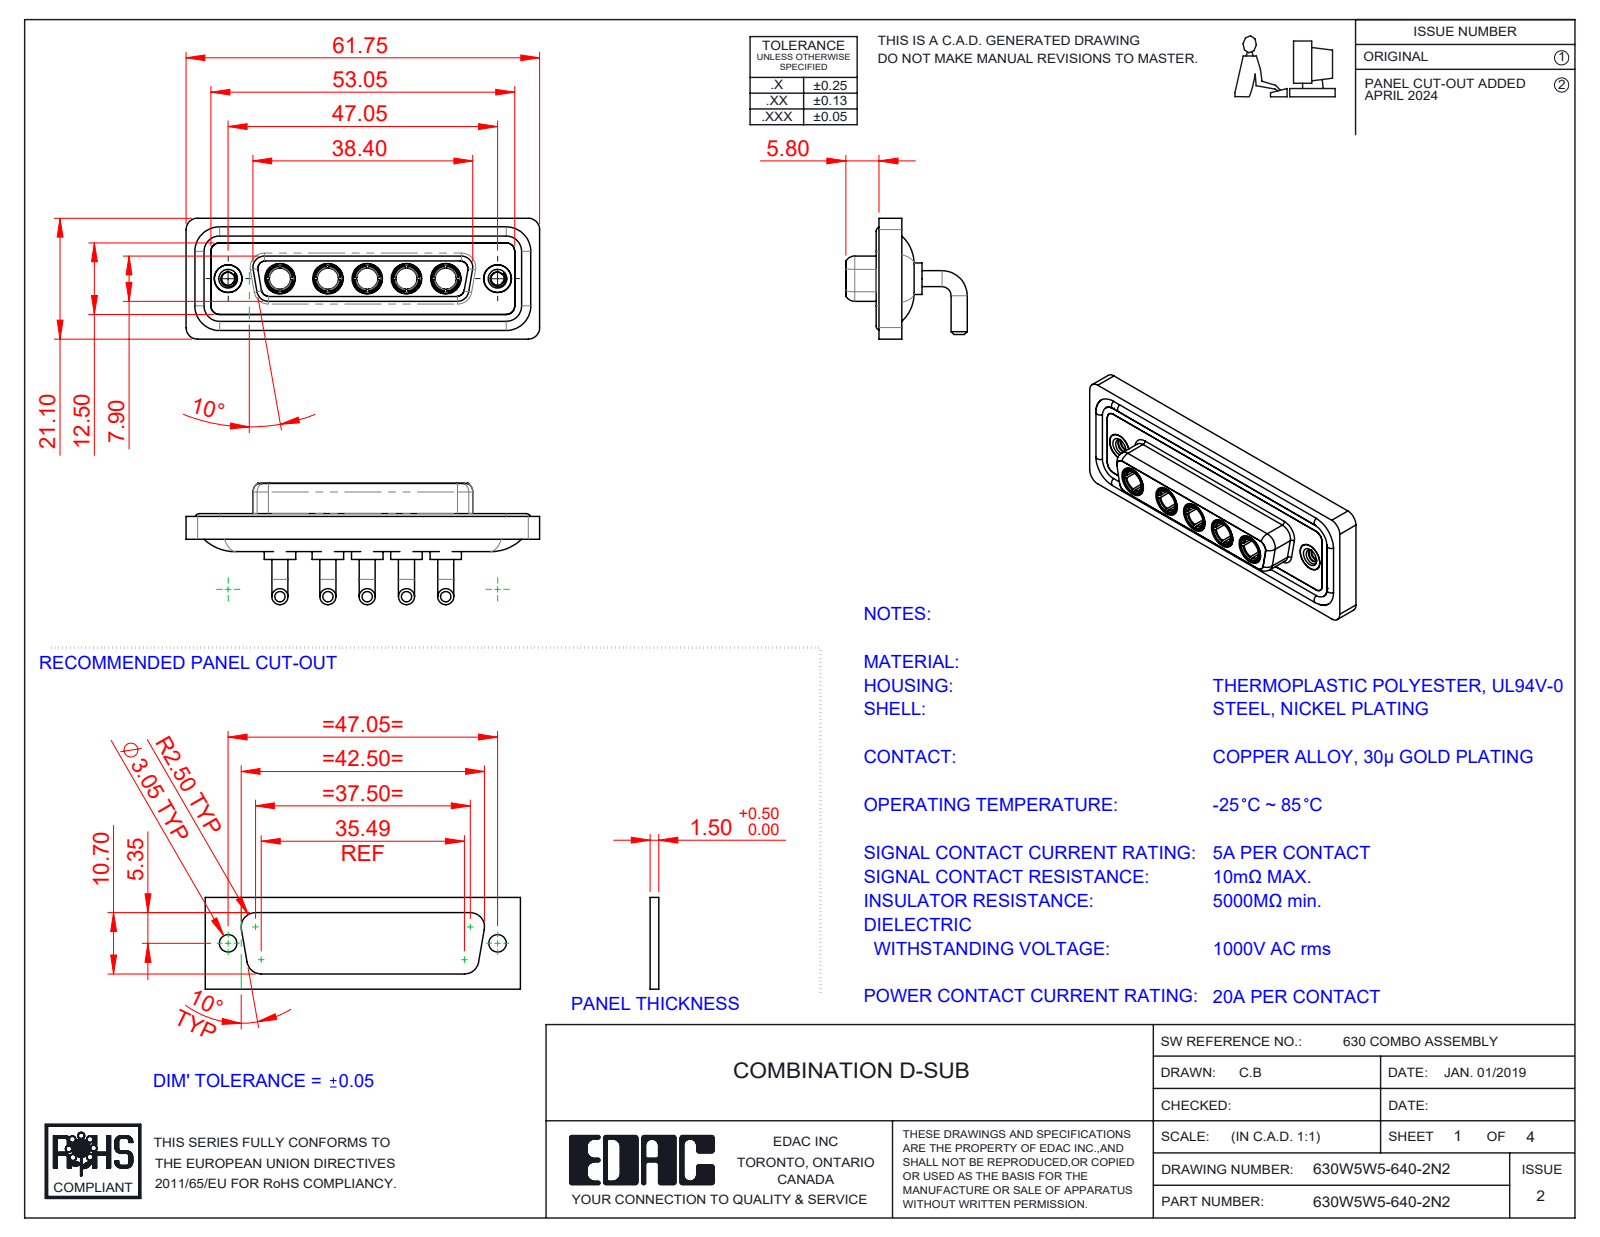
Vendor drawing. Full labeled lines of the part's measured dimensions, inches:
Part name (STEP PRODUCT): Power Socket_20A RA; 630W5W5-640-2N2; 630Combo Shell Front_25 Contacts; 630Combo Waterproof Housing_25 Contacts (+3 more)
STEP written by: SolidWorks 2023 (CONFIG_CONTROL_DESIGN)
Units: inches
Bodies: 17 solids, 776 faces (250 planar, 313 cylindrical, 213 other)
Overall size (bounding box): 2.431 × 0.835 × 0.831
Volume: 0.515 in³ · Surface area: 21.41 in²
Round holes (diameter × count): ⌀0.191 ×7, ⌀0.146 ×5, ⌀0.209 ×5, ⌀0.089 ×2, ⌀0.157 ×2, ⌀0.159 ×2, ⌀0.197 ×2
Round bosses / shafts (diameter × count): ⌀0.11 ×10, ⌀0.217 ×5, ⌀0.205 ×5, ⌀0.195 ×5, ⌀0.187 ×5, ⌀0.148 ×5, ⌀0.063 ×4, ⌀0.195 ×2
Partial cylindrical surfaces — rounded edges, fillets, slot ends (radius × count): R0.059 ×18, R0.079 ×18, R0.053 ×8, R0.063 ×8, R0.083 ×5, R0.01 ×4, R0.02 ×4, R0.024 ×4
Main face-to-face distances: 0.016, 0.071, 0.161, 0.043, 0.059, 0.098, 0.122, 0.146, 0.063, 0.114
Hole centre spacings: 0.27, 0.356, 1.496, 0.27, 0.33, 0.54, 0.541, 0.6
